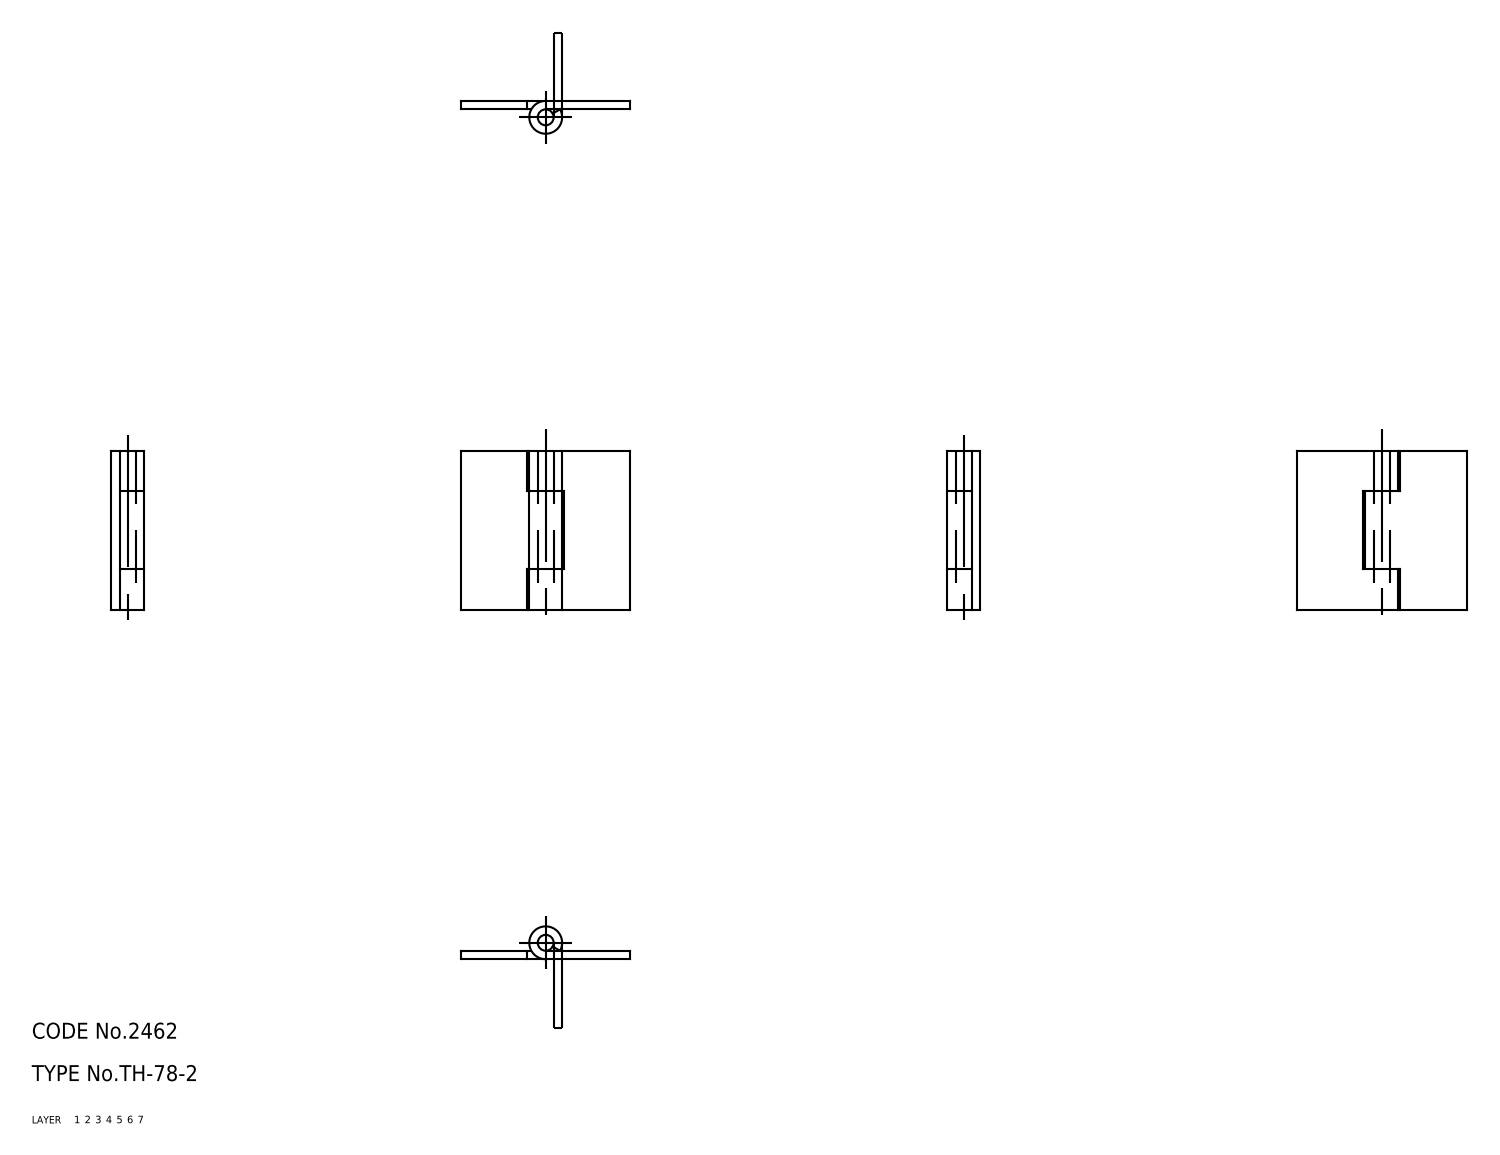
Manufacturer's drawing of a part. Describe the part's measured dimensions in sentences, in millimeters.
The part is named "hinge piece_B; hinge piece_A; shaft; TH_78_2_16622_36". Its 3-D file was written by "CADfix (AUTOMOTIVE_DESIGN)". It is 3 solids with 30 faces: 0 planar, 0 cylindrical and 30 other. Overall it measures 32 by 30 by 6.2 millimeters. Its volume is 2 154 cubic millimeters and its surface area 3 145 square millimeters.
